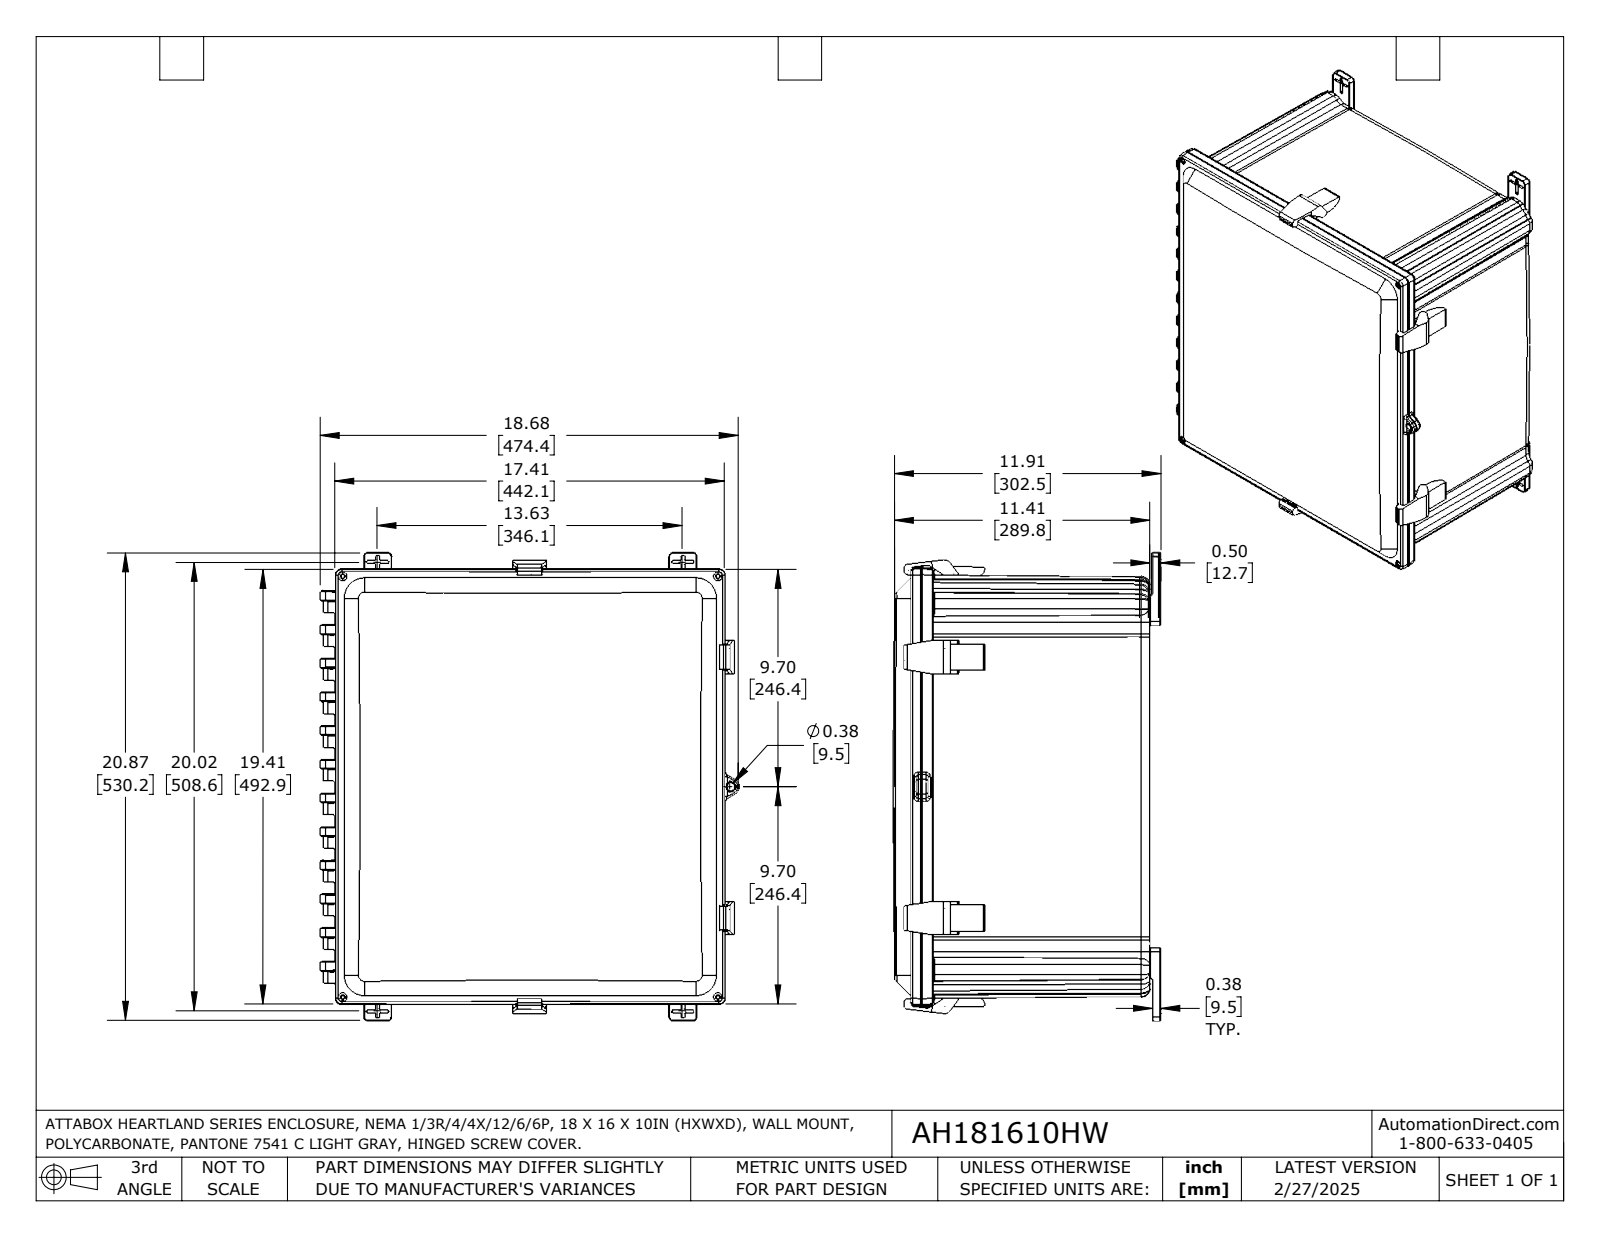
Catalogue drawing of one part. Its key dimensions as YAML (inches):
part_name: "AH181610HW"
step_written_by: "SolidWorks 2024 (AUTOMOTIVE_DESIGN)"
units: inches
bodies: {solids: 10, faces: 3255, planar: 890, cylindrical: 1058, other: 1307}
overall_size: [20.875, 18.676, 11.908]
volume: 257.7
surface_area: 3065
round_holes:
  - {diameter: 0.156, count: 8}
  - {diameter: 0.195, count: 4}
  - {diameter: 0.313, count: 4}
  - {diameter: 0.39, count: 4}
  - {diameter: 0.327, count: 1}
  - {diameter: 0.375, count: 1}
  - {diameter: 0.45, count: 1}
round_bosses_or_shafts:
  - {diameter: 0.25, count: 4}
  - {diameter: 0.313, count: 1}
partial_cylinders:
  - {radius: 0.035, count: 164}
  - {radius: 0.065, count: 139}
  - {radius: 0.05, count: 119}
  - {radius: 0.03, count: 108}
  - {radius: 0.02, count: 88}
  - {radius: 0.025, count: 48}
  - {radius: 0.008, count: 24}
  - {radius: 0.01, count: 23}
face_to_face_distances: [0.14, 10.14, 10, 0.187, 0.5, 0.14, 0.43, 0.29, 10.64, 9.64]
hole_center_spacings: [15.55, 16.75, 15.268, 22.936, 0.442, 1.768, 2.21, 13.941]
